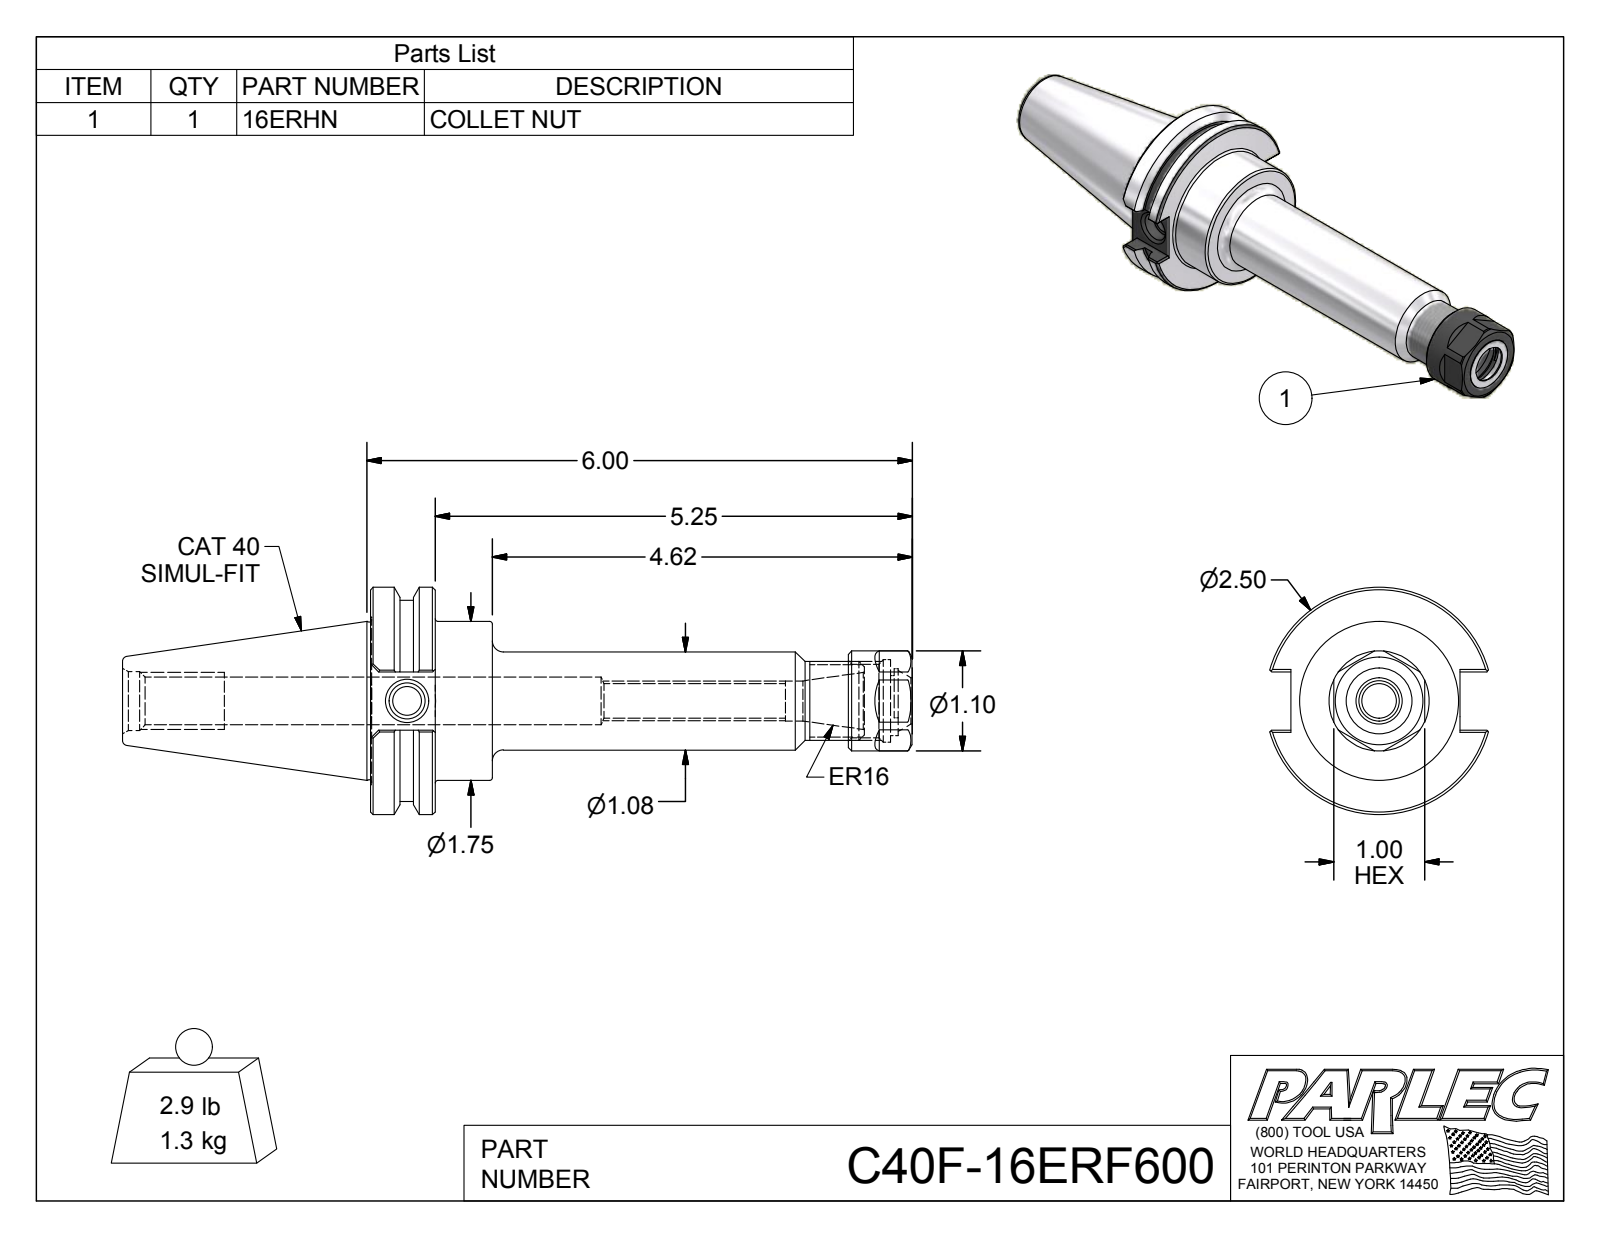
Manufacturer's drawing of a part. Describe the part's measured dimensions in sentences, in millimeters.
The part is named "C40F-16ER6-1; 16ERHN; C40F-16ERF600". Its 3-D file was written by "Autodesk Inventor 2016 (AUTOMOTIVE_DESIGN)". It is 2 solids with 112 faces: 50 planar, 22 cylindrical and 40 other. Overall it measures 220.66 by 63.5 by 61.11 millimeters. Its volume is 177 158 cubic millimeters and its surface area 38 929 square millimeters. Round holes: 1 of diameter 8, 1 of diameter 9.73, 1 of diameter 10.13, 1 of diameter 11.18, 1 of diameter 12.4, 1 of diameter 13.39, 1 of diameter 16.46, 1 of diameter 17.02, 1 of diameter 20.5, 1 of diameter 23. Round bosses or shafts: 1 of diameter 63.5, 1 of diameter 56.26, 1 of diameter 44.45, 1 of diameter 28, 1 of diameter 27.43, 1 of diameter 22. Partial cylindrical surfaces (rounded edges, fillets, slot ends): 1 of radius 7.24, 1 of radius 9. The main face-to-face distances are 18.04, 34.04, 16, 151.39, 133.35, 117.35, 25.14, 145.69, 127.65, 111.65. The hole center spacings are 1.52.
